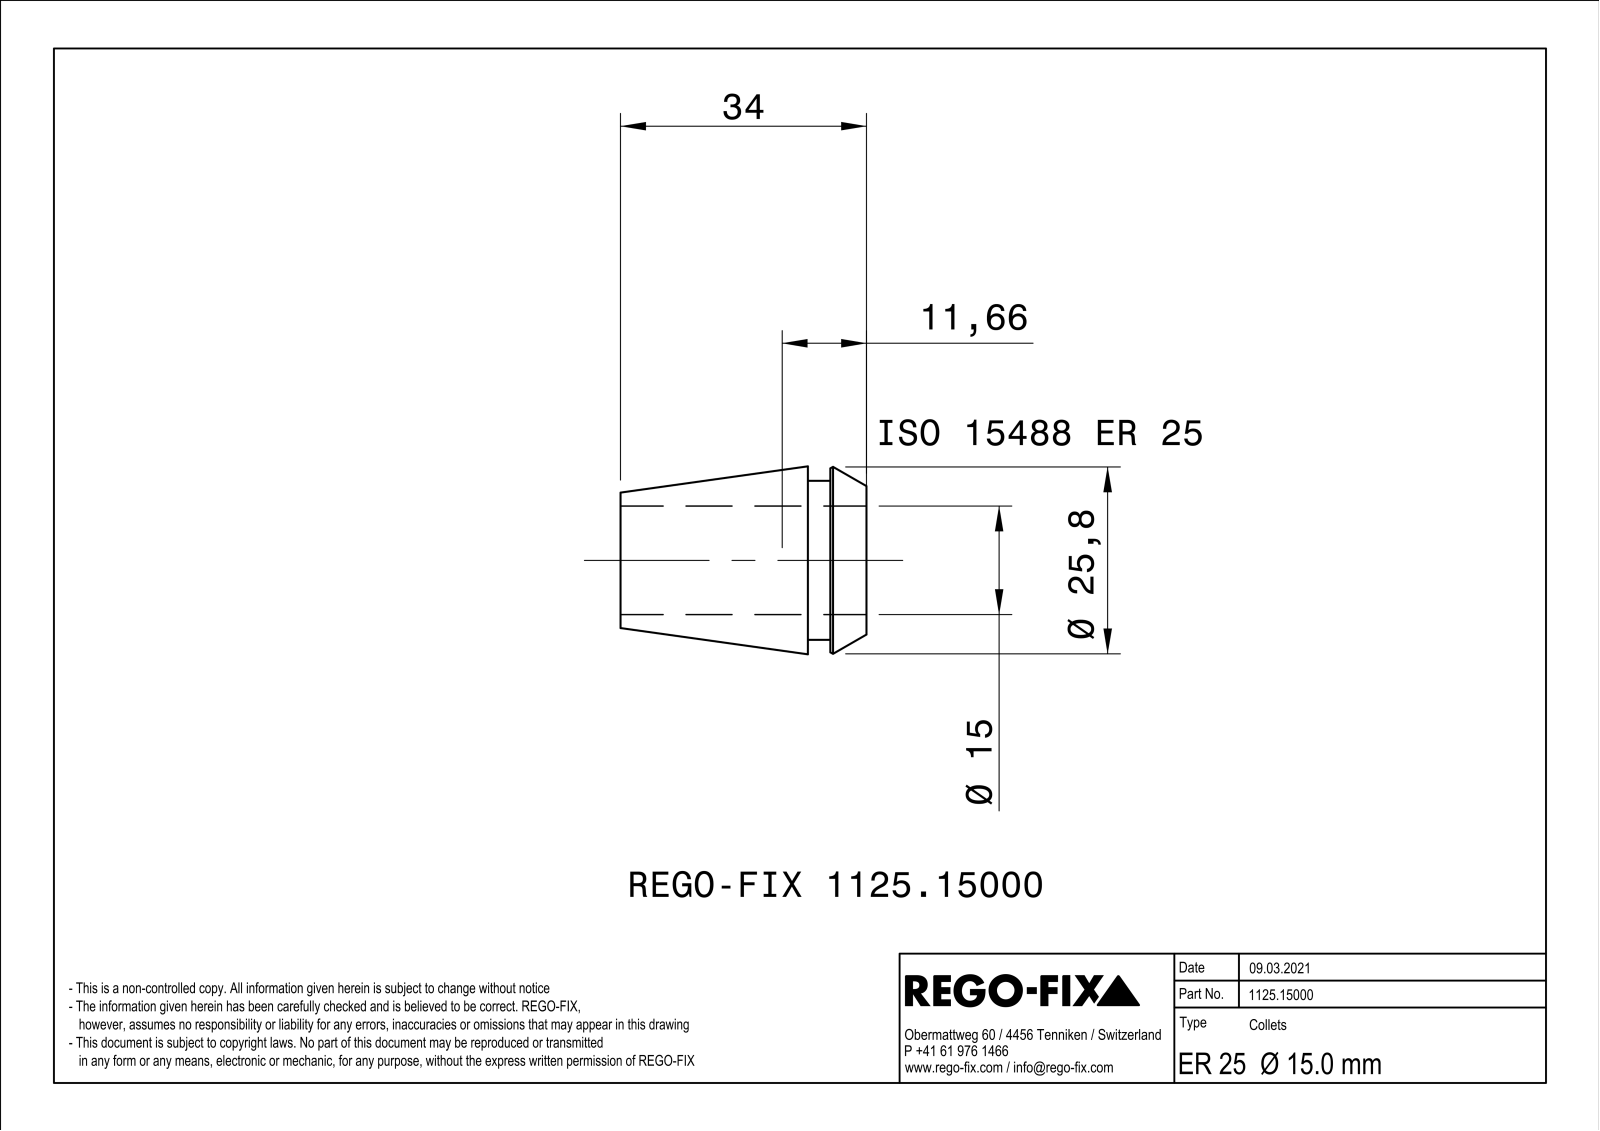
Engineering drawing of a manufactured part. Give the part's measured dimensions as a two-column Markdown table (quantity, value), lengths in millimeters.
| quantity | value |
| --- | --- |
| part name | NOCUT |
| STEP written by | SIEMENS PLM Software Solid Edge ST10 (AUTOMOTIVE_DESIGN) |
| units | millimeters |
| bodies | 1 solid, 177 faces (72 planar, 25 cylindrical, 80 other) |
| overall size | 34 × 25.99 × 25.99 |
| volume | 6 147 mm³ |
| surface area | 7 381 mm² |
| round holes (diameter × count) | 15 × 1 |
| round bosses / shafts (diameter × count) | 22 × 1 |
| partial cylindrical surfaces (radius × count) | 0.4 × 8 |
| main face-to-face distances | 0.8, 8.1, 5, 3.1, 34, 29, 25.9 |
